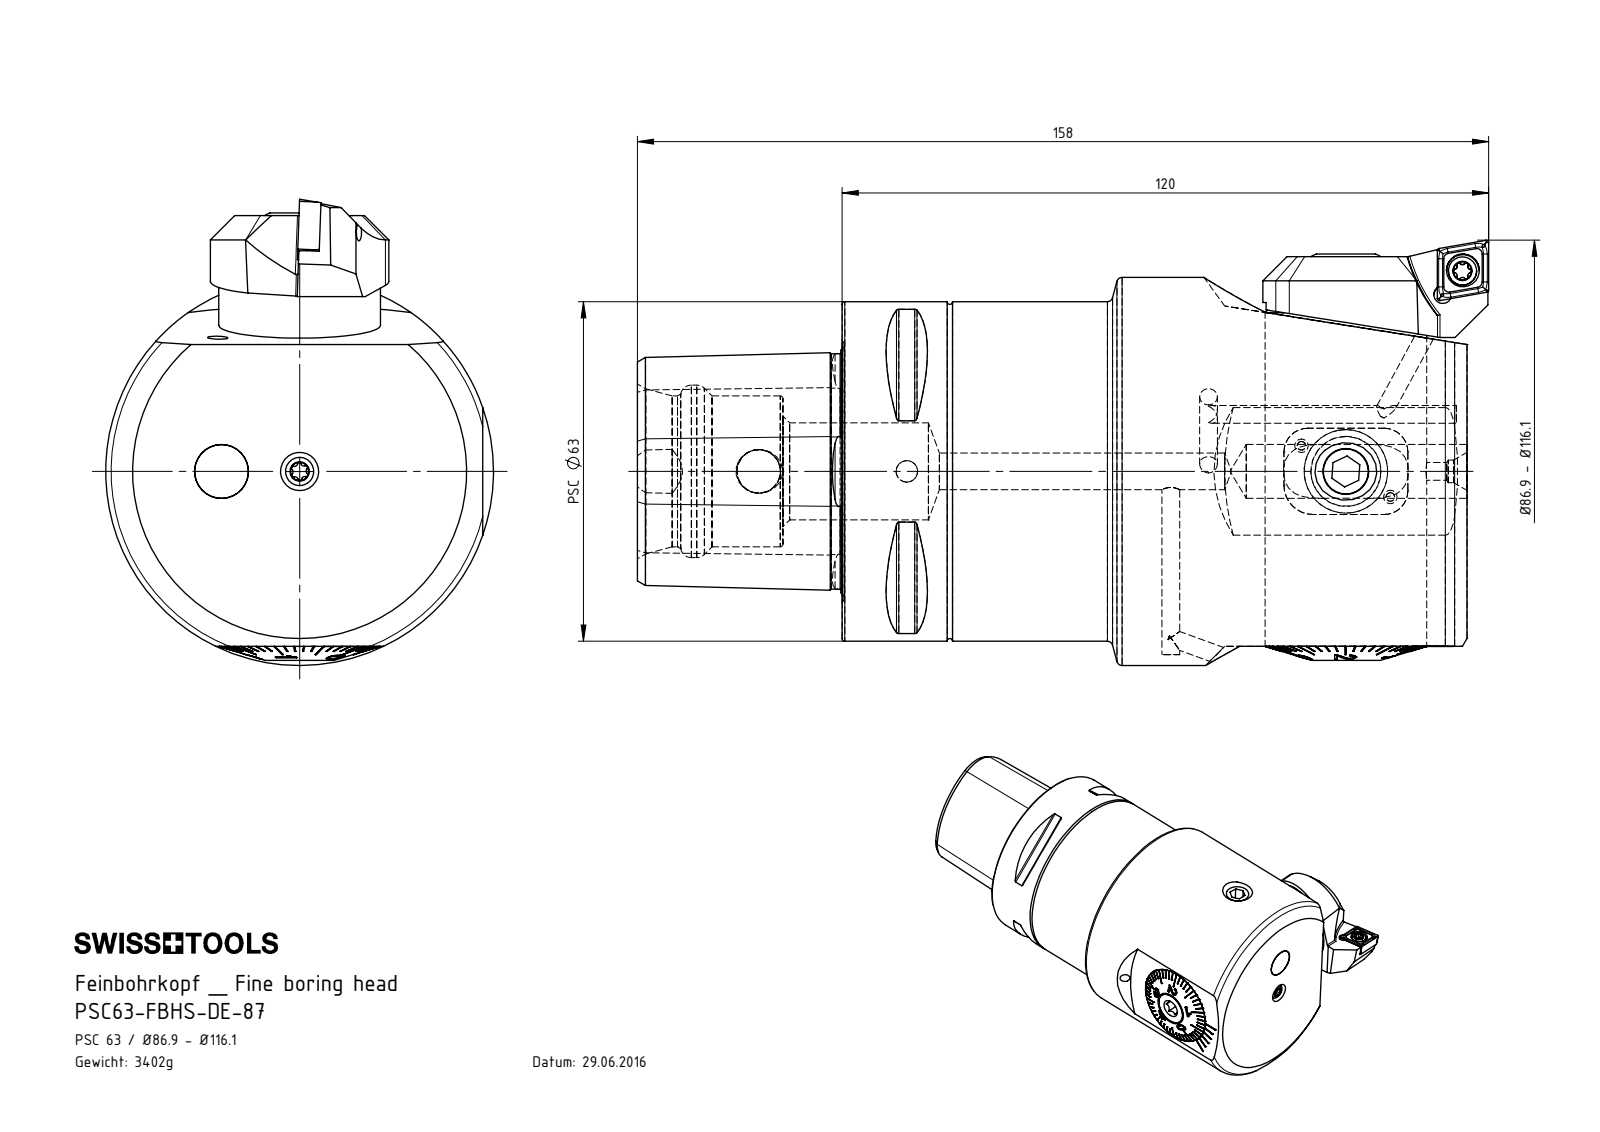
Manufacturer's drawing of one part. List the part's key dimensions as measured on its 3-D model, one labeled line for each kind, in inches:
Part name (STEP PRODUCT): ISO 4026 - M10 x 16; F55-BG1.012.012_A; A55-BG2.011.016_D; PEF-DA1.011.017_A (+8 more)
STEP written by: SolidWorks 2017 (AUTOMOTIVE_DESIGN)
Units: inches
Bodies: 20 solids, 795 faces (412 planar, 146 cylindrical, 237 other)
Overall size (bounding box): 6.063 × 3.006 × 2.835
Volume: 26 in³ · Surface area: 111.7 in²
Round holes (diameter × count): ⌀0.13 ×7, ⌀0.165 ×3, ⌀0.063 ×2, ⌀0.087 ×2, ⌀0.335 ×2, ⌀0.512 ×2, ⌀0.157 ×1, ⌀0.197 ×1, ⌀0.268 ×1, ⌀0.315 ×1, ⌀0.319 ×1, ⌀0.374 ×1
Round bosses / shafts (diameter × count): ⌀0.075 ×6, ⌀0.394 ×2, ⌀0.15 ×2, ⌀0.079 ×2, ⌀2.835 ×1, ⌀2.48 ×1, ⌀1.181 ×1, ⌀1.18 ×1
Partial cylindrical surfaces — rounded edges, fillets, slot ends (radius × count): R0.02 ×10, R0.013 ×6, R0.023 ×6, R0.043 ×6, R0.047 ×6, R0.177 ×4, R0.126 ×3, R0.173 ×3
Main face-to-face distances: 4.567, 0.256, 0.209, 0.047, 0.11, 0.098, 0.146, 2.197, 2.307, 2.406
Hole centre spacings: 0.375, 0.553, 0.571, 0.75, 1.024, 1.083, 1.28, 2.89
